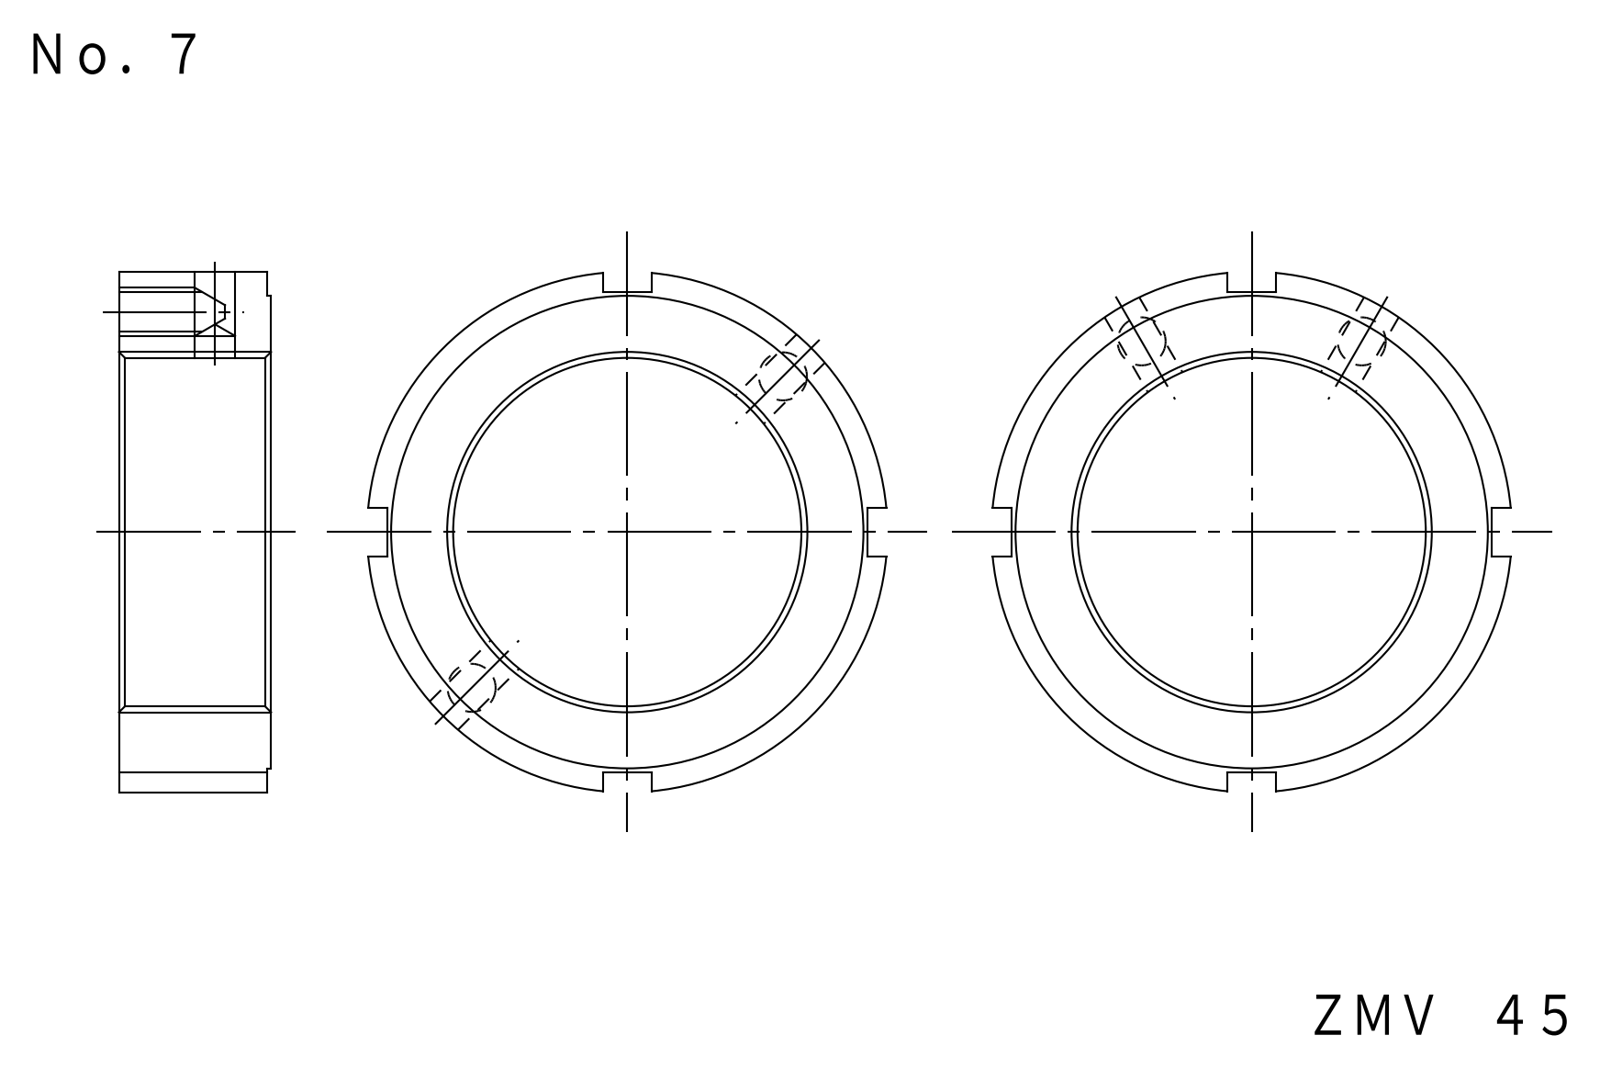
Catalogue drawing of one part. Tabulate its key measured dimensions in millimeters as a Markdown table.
| quantity | value |
| --- | --- |
| part name | FKD ZMV 45 |
| STEP written by | Autodesk Inventor 2011 (AUTOMOTIVE_DESIGN) |
| units | millimeters |
| bodies | 1 solid, 25 faces (15 planar, 10 cylindrical, 0 other) |
| overall size | 64.72 × 64.72 × 19 |
| volume | 30 680 mm³ |
| surface area | 10 714 mm² |
| round holes (diameter × count) | 4.92 × 2, 5 × 1, 45 × 1 |
| round bosses / shafts (diameter × count) | 65 × 1, 59 × 1 |
| main face-to-face distances | 19, 0.5, 18.5, 27, 33, 60, 6 |
| hole center spacings | 27.51, 55.01 |
